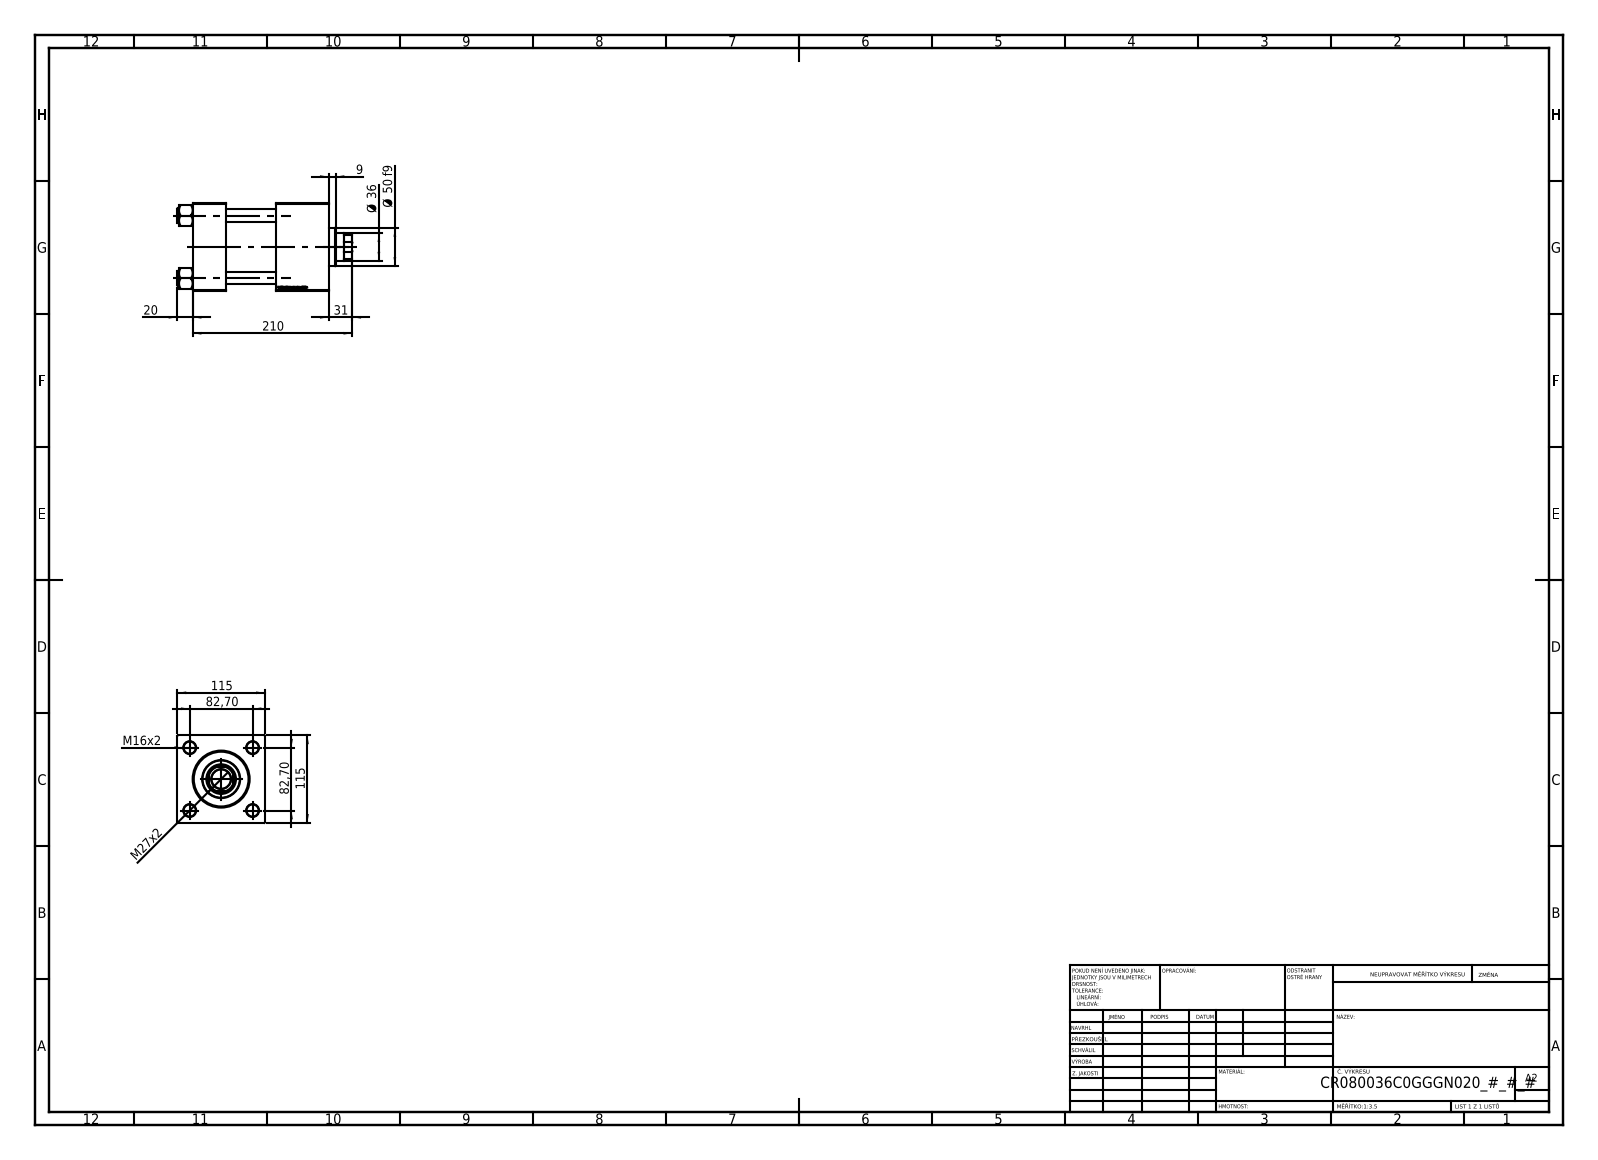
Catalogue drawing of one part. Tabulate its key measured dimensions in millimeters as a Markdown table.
| quantity | value |
| --- | --- |
| part name | V215CR_VCP_C; V215CR_C_Body; V215CR_C_TYCINKA; V215_VC_A (+1 more) |
| STEP written by | SolidWorks 2019 (CONFIG_CONTROL_DESIGN) |
| units | millimeters |
| bodies | 11 solids, 1197 faces (574 planar, 87 cylindrical, 536 other) |
| overall size | 230 × 115 × 115 |
| volume | 1 786 000 mm³ |
| surface area | 268 442 mm² |
| round holes (diameter × count) | 16 × 4, 7 × 2, 26.44 × 2, 35 × 2, 25.5 × 1, 36 × 1, 39 × 1, 61 × 1, 72 × 1, 80 × 1 |
| round bosses / shafts (diameter × count) | 19 × 4, 86 × 1, 50 × 1 |
| partial cylindrical surfaces (radius × count) | 17.5 × 1 |
| main face-to-face distances | 115, 44, 179, 135, 110, 69, 66, 20, 150.3, 106.3 |
| hole center spacings | 58.48, 82.7, 116.96, 111 |
